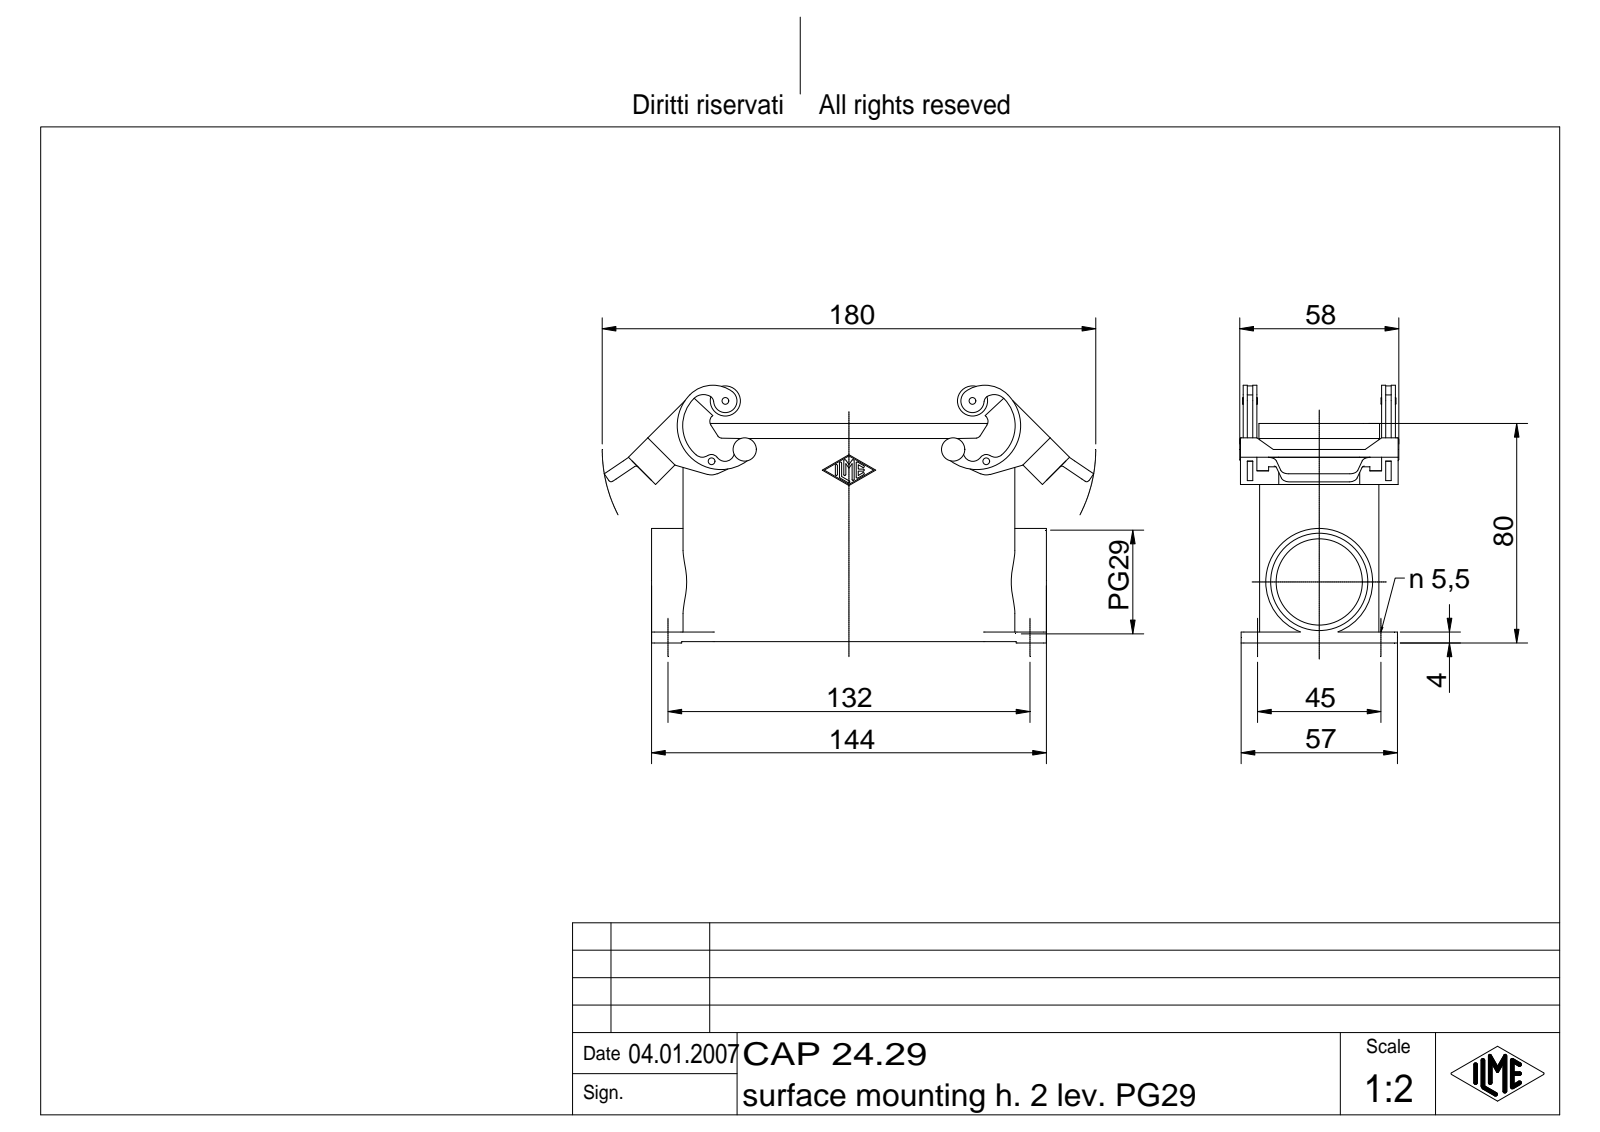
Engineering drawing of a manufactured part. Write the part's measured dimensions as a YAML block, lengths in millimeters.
part_name: "CAP 24.29"
step_written_by: "Autodesk Inventor 7 (AUTOMOTIVE_DESIGN)"
units: millimeters
bodies: {solids: 1, faces: 753, planar: 193, cylindrical: 207, other: 353}
overall_size: [178.49, 93.94, 58]
volume: 139424
surface_area: 82812
round_holes:
  - {diameter: 2, count: 4}
  - {diameter: 5.5, count: 4}
  - {diameter: 2.5, count: 2}
  - {diameter: 31.48, count: 1}
  - {diameter: 35.48, count: 1}
round_bosses_or_shafts:
  - {diameter: 11, count: 2}
  - {diameter: 5, count: 2}
  - {diameter: 3, count: 2}
  - {diameter: 38.98, count: 1}
partial_cylinders:
  - {radius: 1, count: 20}
  - {radius: 0.38, count: 14}
  - {radius: 3, count: 12}
  - {radius: 6, count: 8}
  - {radius: 2.5, count: 6}
  - {radius: 1.5, count: 4}
  - {radius: 2, count: 4}
  - {radius: 3.5, count: 4}
face_to_face_distances: [3, 40.5, 43.5, 37.5, 3.5, 4, 0.75, 50.5, 40.75, 3.75]
hole_center_spacings: [22.56, 45, 97.67, 132, 139.46, 90.14, 100.18]
